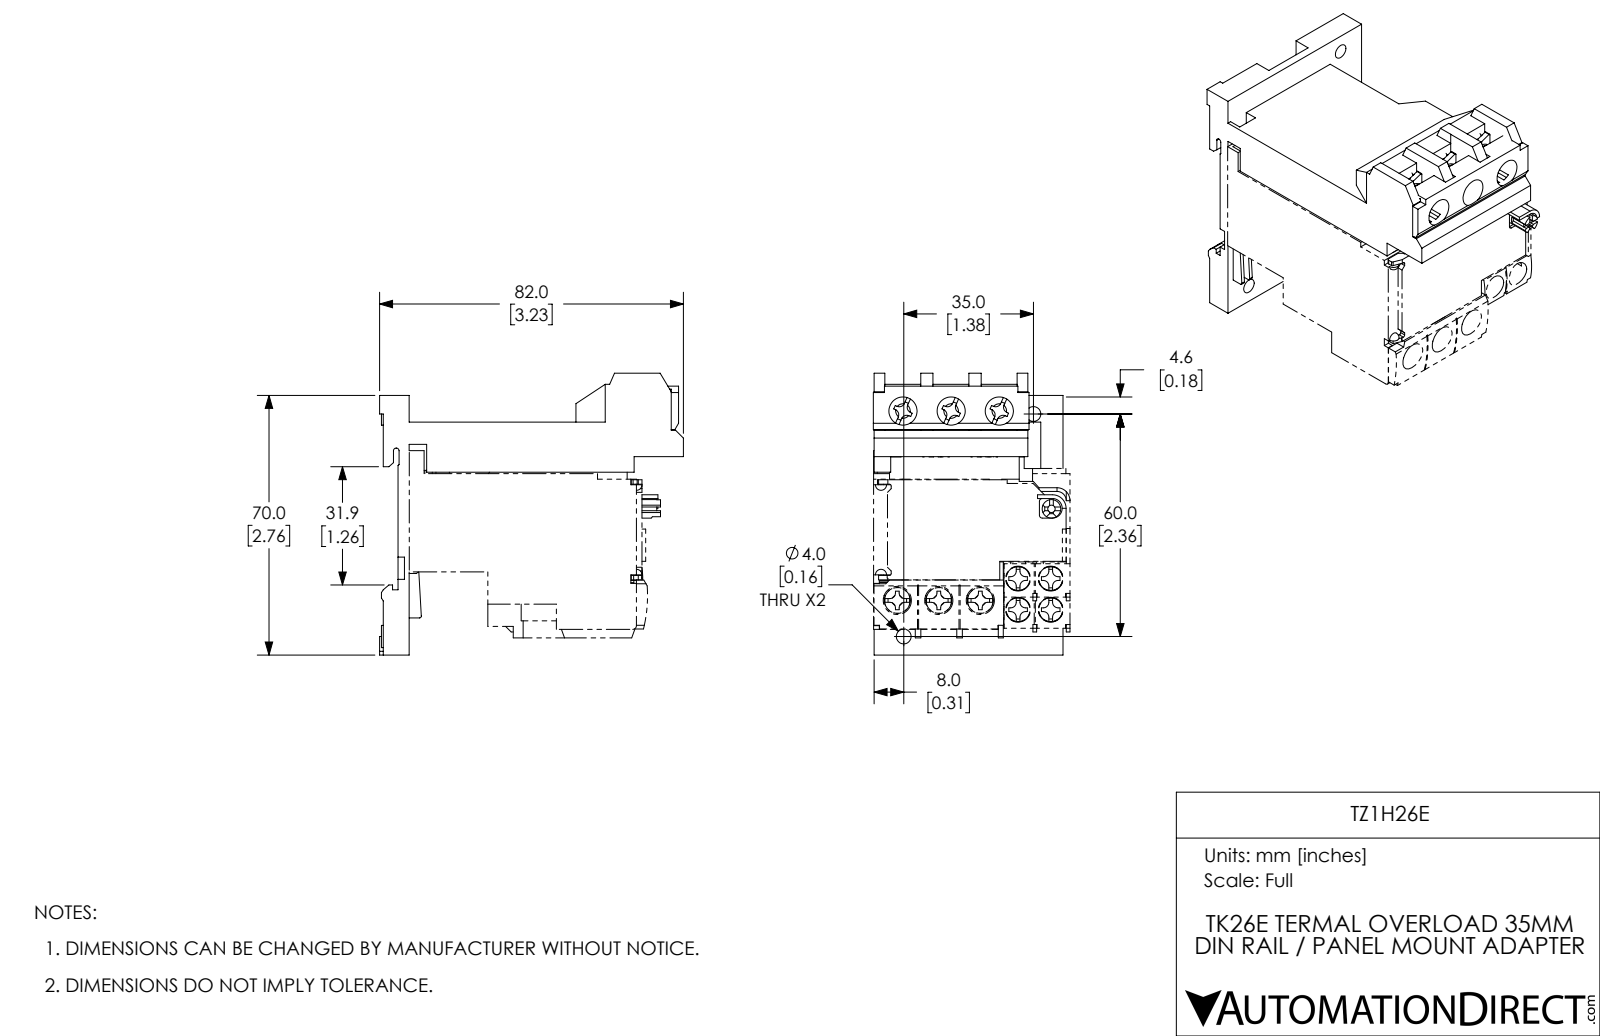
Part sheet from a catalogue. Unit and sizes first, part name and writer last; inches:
Units: inches
Overall size (bounding box): 3.228 × 2.992 × 2.016
Round holes (diameter × count): ⌀0.157 ×5, ⌀0.138 ×3, ⌀0.299 ×3, ⌀0.205 ×2
Round bosses / shafts (diameter × count): ⌀0.236 ×2, ⌀0.189 ×2, ⌀0.378 ×1
Partial cylindrical surfaces — rounded edges, fillets, slot ends (radius × count): R0.02 ×14, R0.059 ×12, R0.079 ×6, R0.028 ×2, R0.043 ×2, R0.189 ×2, R0.016 ×1, R0.031 ×1
Main face-to-face distances: 0.016, 0.039, 0.079, 0.024, 0.063, 0.094, 0.055, 1.732, 0.102, 0.087
Hole centre spacings: 0.512, 0.363, 0.874, 1.024, 1.386, 2.394, 2.446, 2.6
Volume: 1.041 in³ · Surface area: 70.09 in²
Bodies: 11 solids, 809 faces (684 planar, 113 cylindrical, 12 other)
Part name (STEP PRODUCT): TZ1H26E
STEP written by: SolidWorks 2017 (AUTOMOTIVE_DESIGN)
